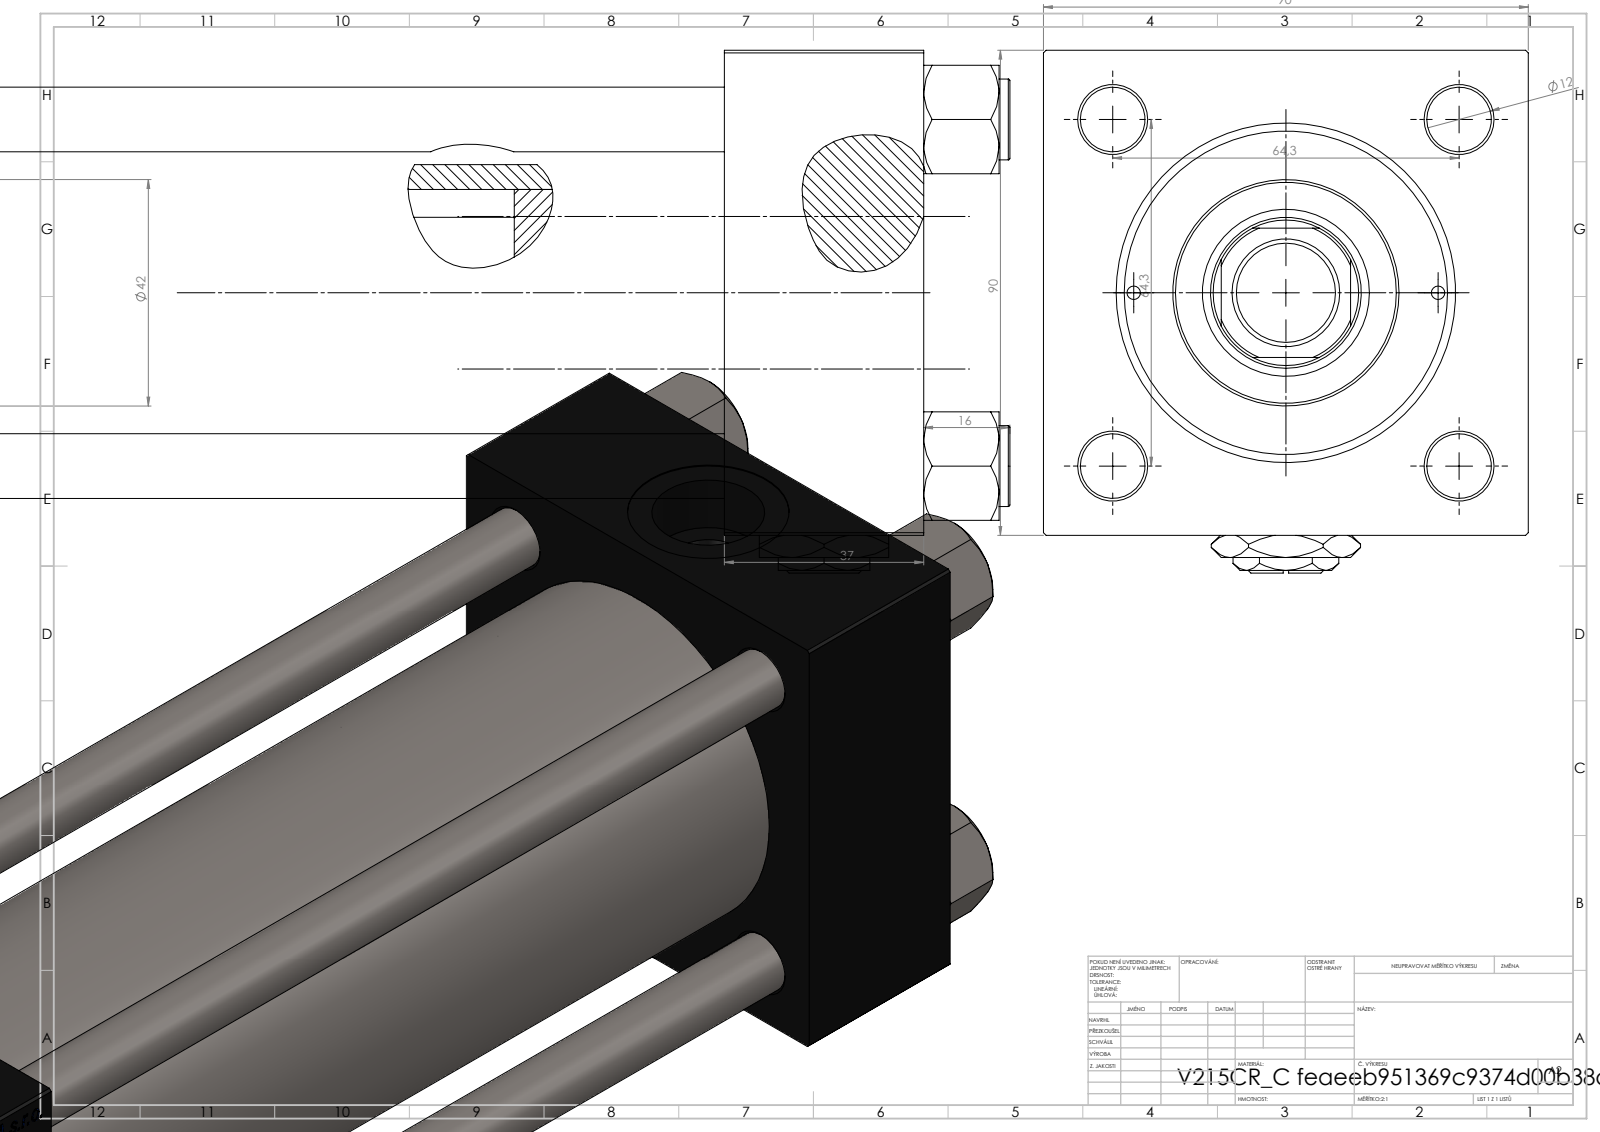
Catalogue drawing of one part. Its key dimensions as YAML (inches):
part_name: "Zatka_pro_OIL_PORT; V215CR_C_TYCINKA; V215CR_VCP_C; NUT_M5_C (+3 more)"
step_written_by: "SolidWorks 2019 (CONFIG_CONTROL_DESIGN)"
units: inches
bodies: {solids: 14, faces: 1270, planar: 580, cylindrical: 106, other: 584}
overall_size: [14.606, 3.819, 3.543]
volume: 72.31
surface_area: 430.9
round_holes:
  - {diameter: 0.472, count: 4}
  - {diameter: 0.098, count: 2}
  - {diameter: 0.276, count: 2}
  - {diameter: 0.825, count: 2}
  - {diameter: 1.181, count: 2}
  - {diameter: 0.728, count: 1}
  - {diameter: 1.102, count: 1}
  - {diameter: 1.22, count: 1}
  - {diameter: 1.969, count: 1}
  - {diameter: 2.362, count: 1}
  - {diameter: 2.48, count: 1}
round_bosses_or_shafts:
  - {diameter: 0.591, count: 4}
  - {diameter: 2.717, count: 1}
  - {diameter: 1.654, count: 1}
  - {diameter: 0.787, count: 1}
  - {diameter: 0.709, count: 1}
partial_cylinders:
  - {radius: 0.531, count: 1}
face_to_face_distances: [3.543, 1.457, 10.157, 11.614, 2.323, 9.291, 7.835, 10.484, 9.028, 1.193]
hole_center_spacings: [1.275, 1.79, 2.531, 2.694, 1.112, 3.58, 2.224, 9.35]
